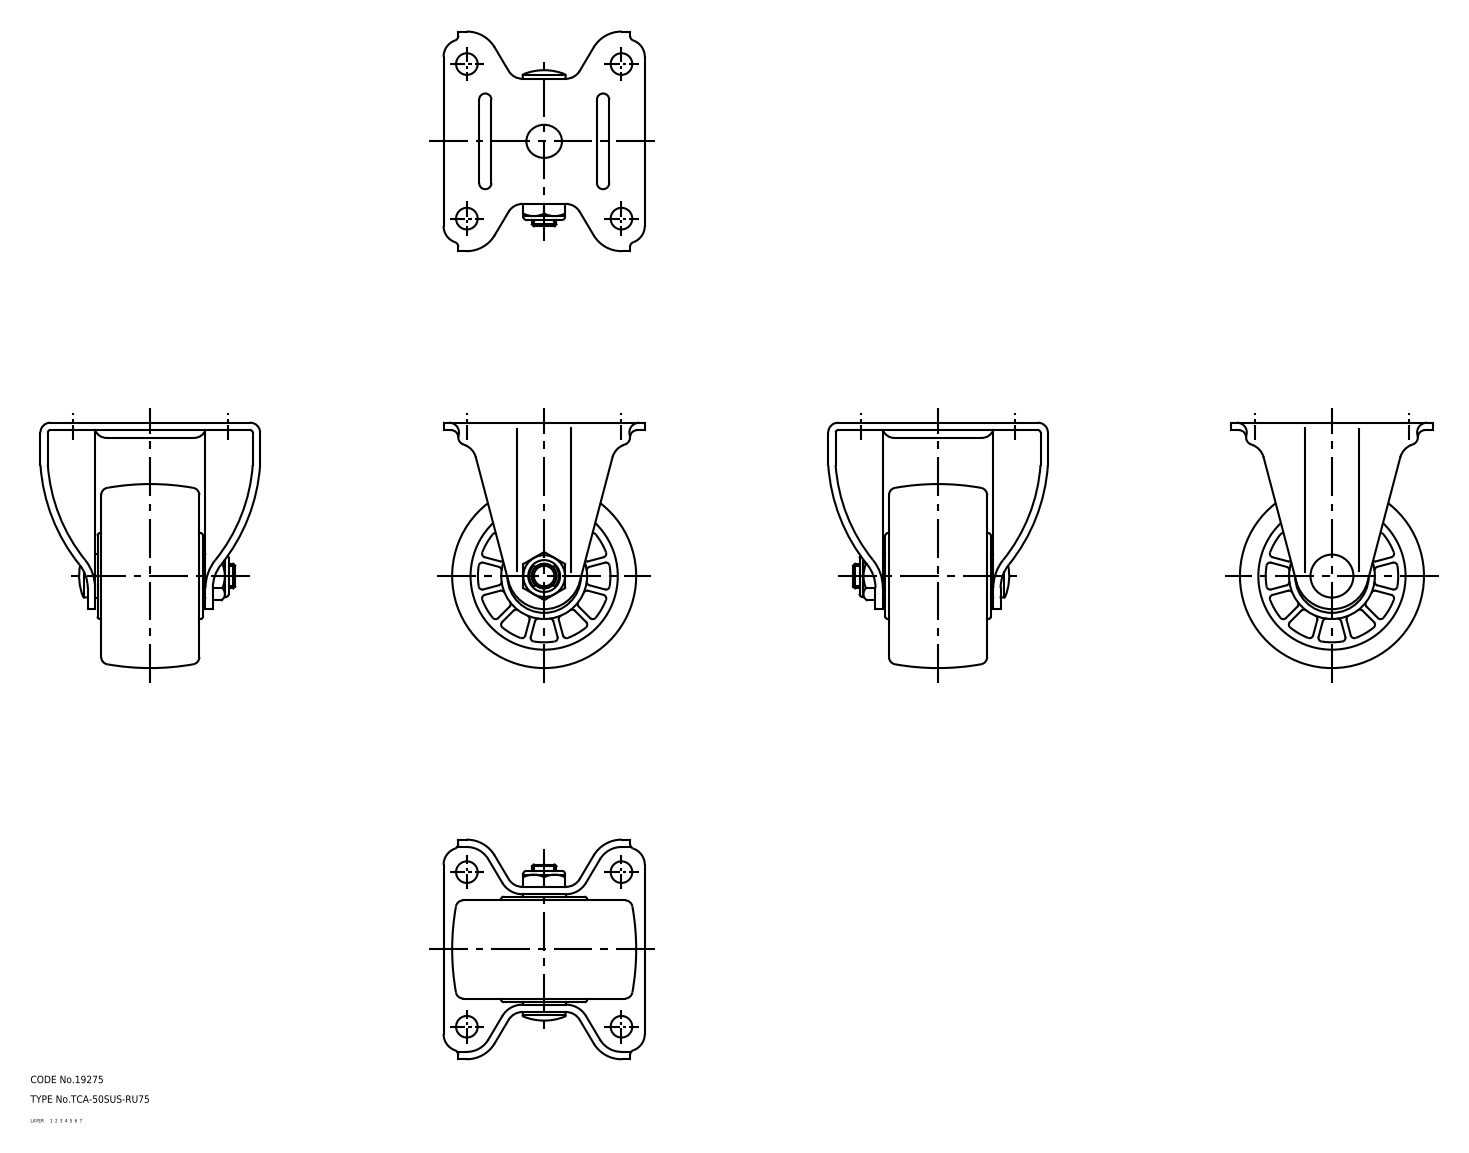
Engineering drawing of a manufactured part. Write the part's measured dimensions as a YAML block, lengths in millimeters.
part_name: "67127657; 67127670; 67127683; 67127696"
step_written_by: "CADfix (AUTOMOTIVE_DESIGN)"
units: millimeters
bodies: {solids: 4, faces: 331, planar: 0, cylindrical: 0, other: 331}
overall_size: [100, 89.5, 82]
volume: 174323
surface_area: 66243
